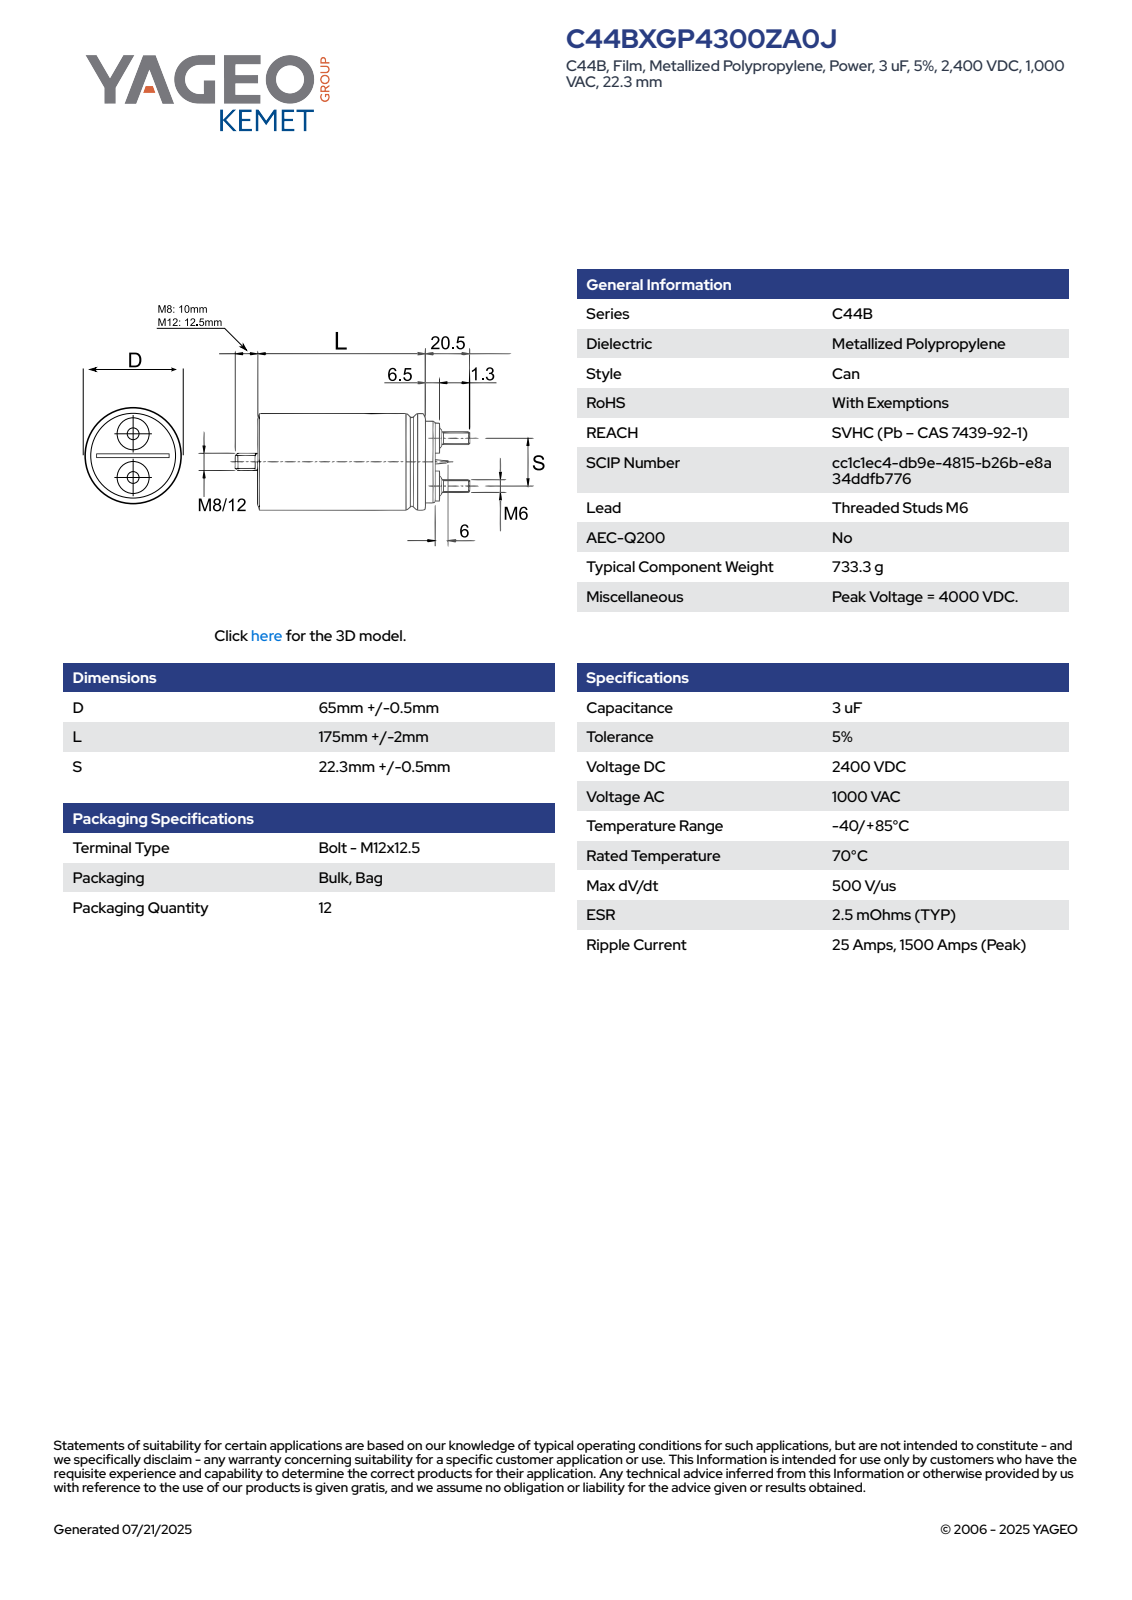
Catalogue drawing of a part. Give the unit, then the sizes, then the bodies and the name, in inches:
Units: inches
Overall size (bounding box): 8.248 × 2.579 × 2.579
Round bosses / shafts (diameter × count): ⌀0.709 ×2, ⌀0.512 ×2, ⌀0.236 ×2, ⌀2.579 ×1, ⌀2.282 ×1, ⌀0.472 ×1
Partial cylindrical surfaces — rounded edges, fillets, slot ends (radius × count): R0.014 ×1, R1.29 ×1
Main face-to-face distances: 7.126, 6.969, 0.157, 0.028, 7.224, 0.256, 0.098, 7.264, 0.295, 0.138
Volume: 36.85 in³ · Surface area: 72.07 in²
Bodies: 1 solid, 117 faces (35 planar, 39 cylindrical, 43 other)
Part name (STEP PRODUCT): CFP_M6_65X175_D65.5L177S22.8
STEP written by: SolidWorks 2014 (AUTOMOTIVE_DESIGN)
